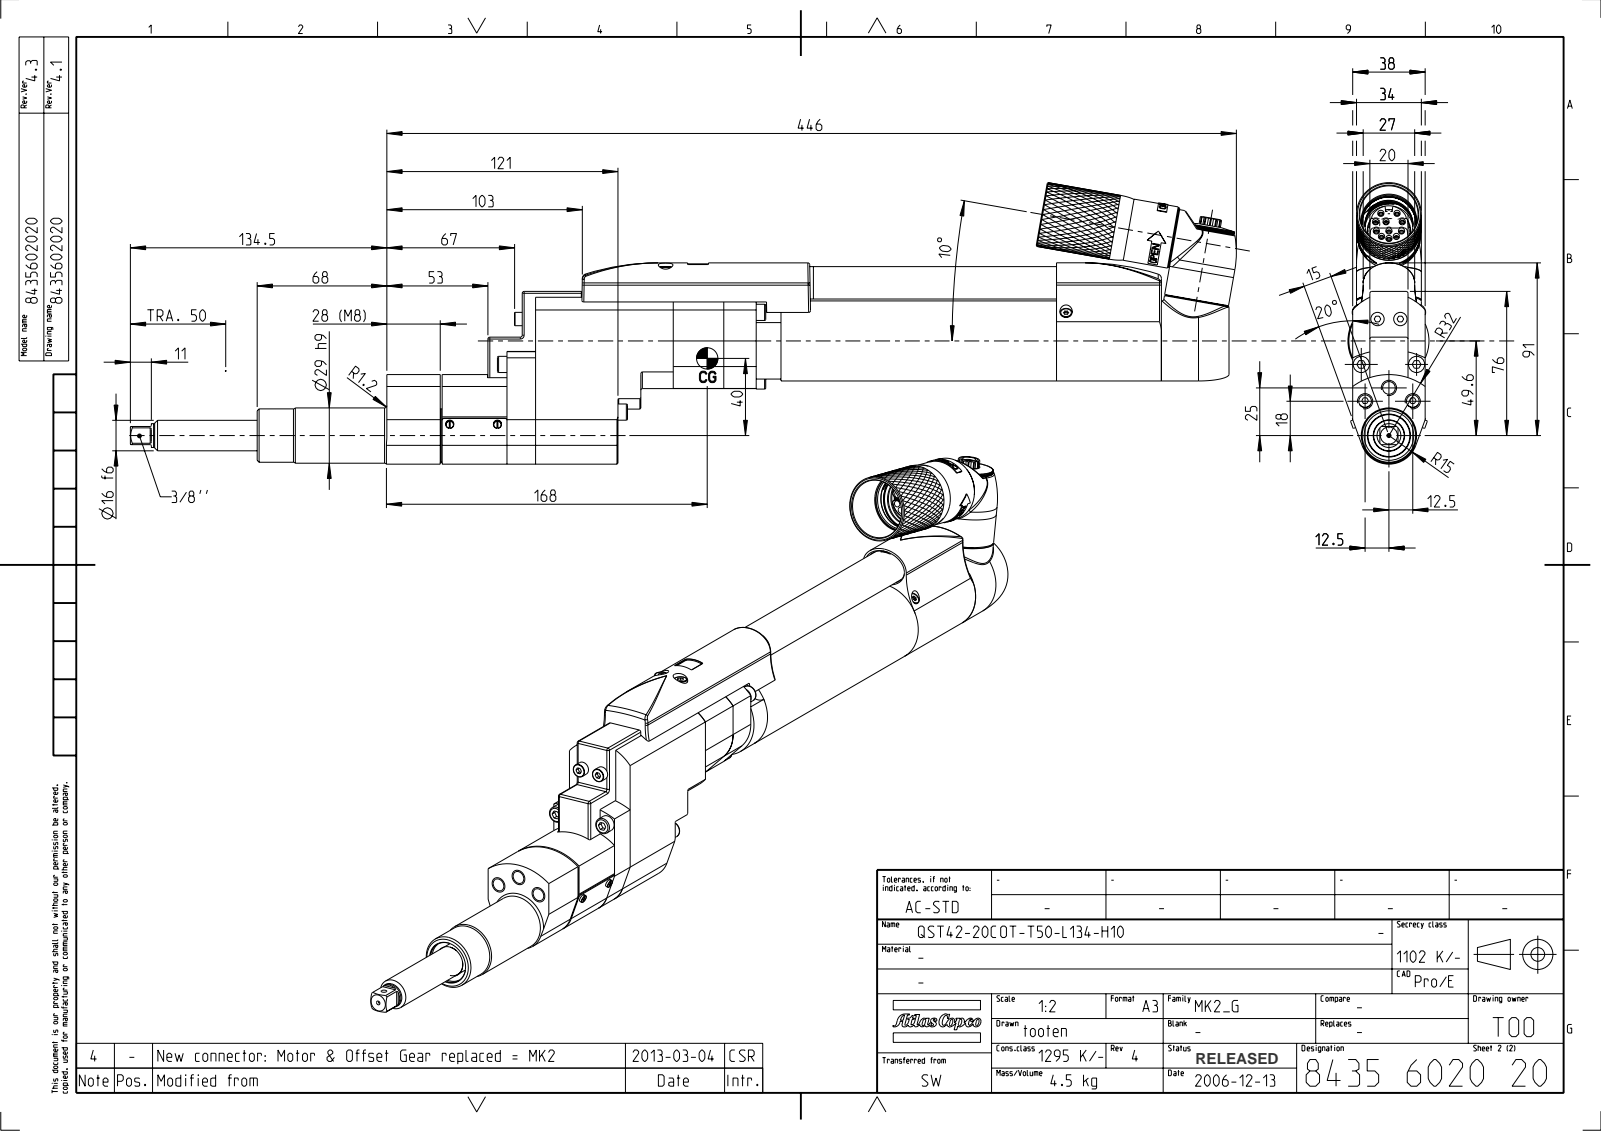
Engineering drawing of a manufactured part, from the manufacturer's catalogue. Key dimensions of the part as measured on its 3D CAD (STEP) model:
Part name (STEP PRODUCT): QST42_REARCOVER_02; QST_CONNECTOR_02; QST42_20_COT_BODY_50; QST42_SOCKETHOLDER_134_10 (+1 more)
STEP written by: PRO/ENGINEER BY PARAMETRIC TECHNOLOGY CORPORATION, 2012420 (CONFIG_CONTROL_DESIGN)
Units: millimetres
Bodies: 7 solids, 3119 faces (1149 planar, 1045 cylindrical, 925 other)
Overall size (bounding box): 580.06 × 147.69 × 42
Volume: 503 758 mm³ · Surface area: 254 804 mm²
Round holes (diameter × count): ⌀3.24 ×10, ⌀3.3 ×9, ⌀3 ×7, ⌀4.5 ×6, ⌀3.5 ×5, ⌀3.92 ×5, ⌀5.3 ×5, ⌀5.5 ×5, ⌀1.4 ×3, ⌀2.46 ×3, ⌀2.94 ×3, ⌀4.3 ×3
Round bosses / shafts (diameter × count): ⌀5 ×8, ⌀8.5 ×7, ⌀3 ×6, ⌀4 ×5, ⌀2.5 ×5, ⌀7 ×4, ⌀4.2 ×4, ⌀2.2 ×4
Partial cylindrical surfaces — rounded edges, fillets, slot ends (radius × count): R1 ×24, R0.2 ×8, R0.5 ×7, R2 ×6, R0.6 ×4, R1.5 ×4, R5.25 ×4, R40 ×4
Main face-to-face distances: 38, 1, 9, 29, 28, 24, 25, 10, 18, 6
Hole centre spacings: 25, 15.92, 19.03, 40.04, 12, 15, 5.05, 13.12
